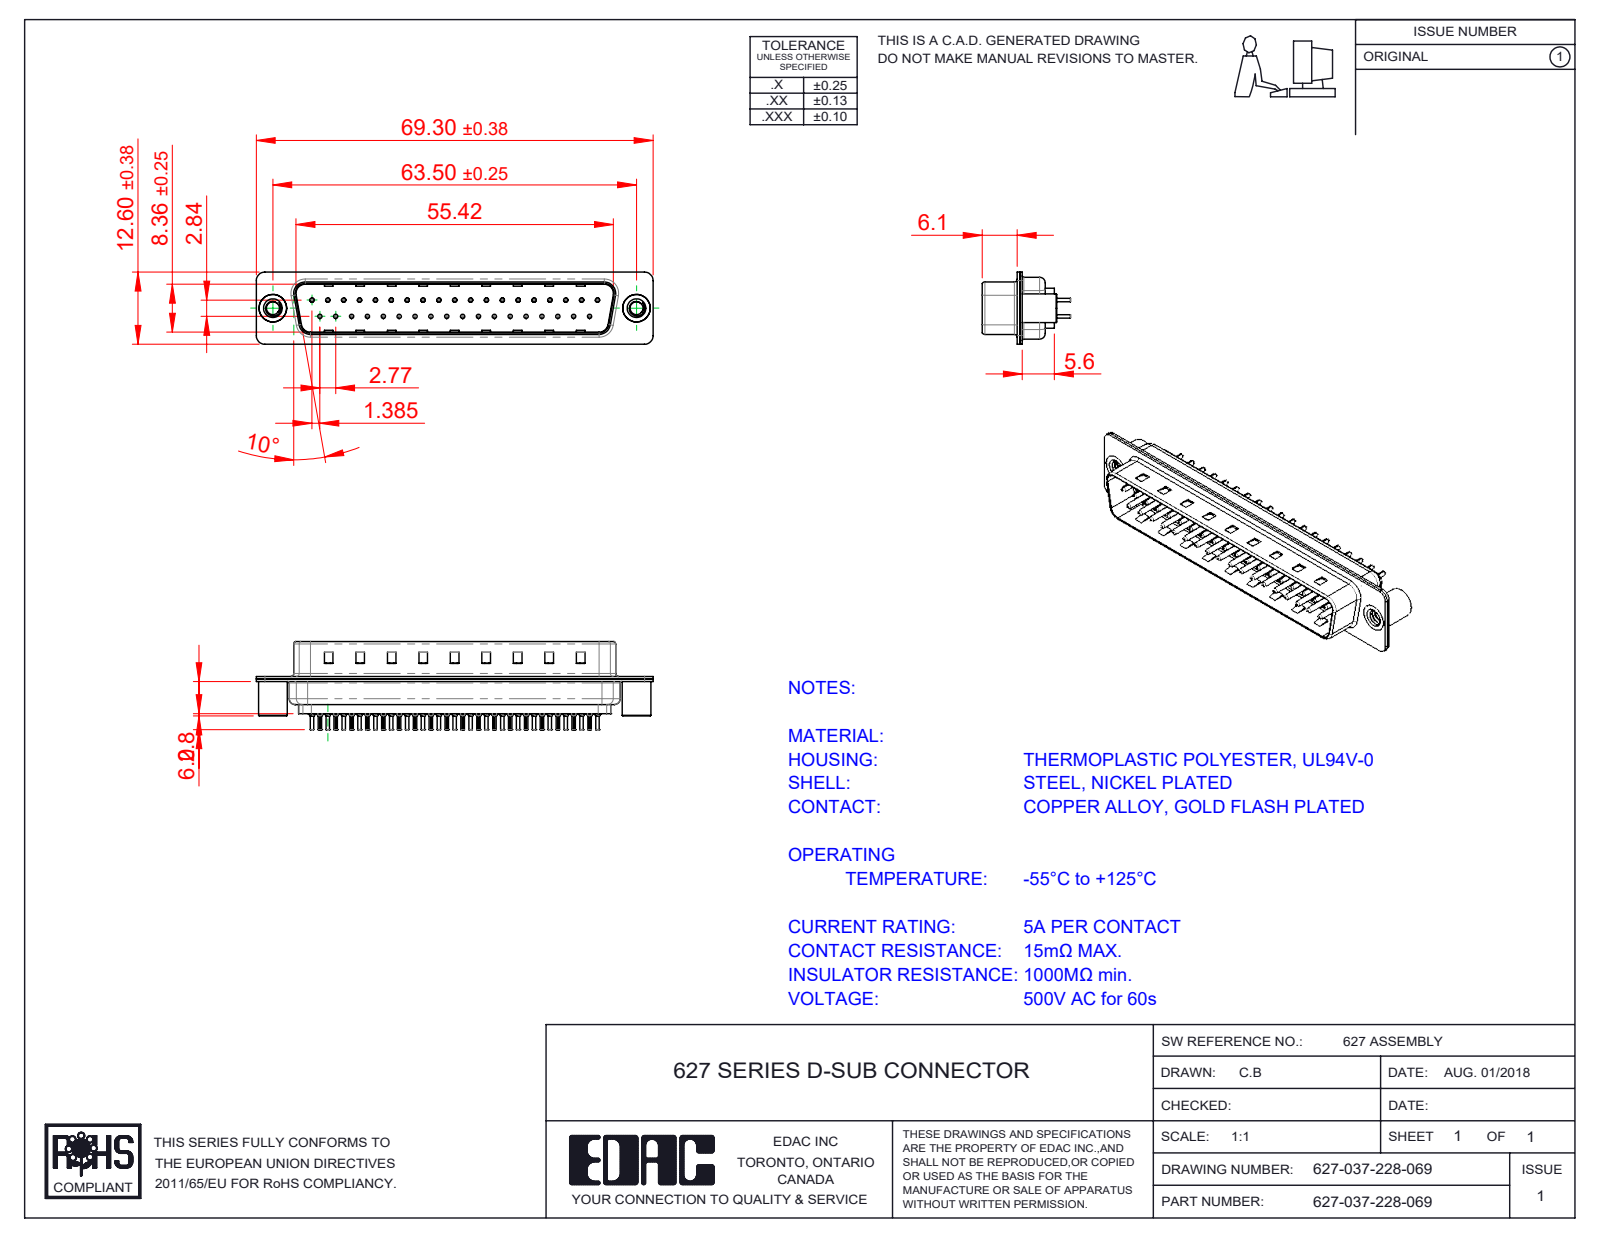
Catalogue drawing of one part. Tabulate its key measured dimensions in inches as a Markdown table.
| quantity | value |
| --- | --- |
| part name | 627-037-228-069; 627 Shell Rear_37 Contacts; 627 Housing_37 FF; 627 4-40 Threaded Standoff BS (+3 more) |
| STEP written by | SolidWorks 2020 (CONFIG_CONTROL_DESIGN) |
| units | inches |
| bodies | 43 solids, 4145 faces (1097 planar, 1609 cylindrical, 1439 other) |
| overall size | 2.728 × 0.74 × 0.496 |
| volume | 0.284 in³ |
| surface area | 19.35 in² |
| round holes (diameter × count) | 0.008 × 37, 0.014 × 37, 0.043 × 37, 0.063 × 37, 0.089 × 2, 0.157 × 2, 0.189 × 2 |
| round bosses / shafts (diameter × count) | 0.079 × 37, 0.059 × 37, 0.03 × 37, 0.024 × 37, 0.197 × 2, 0.193 × 2 |
| partial cylindrical surfaces (radius × count) | 0.004 × 74, 0.059 × 16, 0.079 × 12, 0.02 × 8, 0.063 × 8, 0.01 × 4, 0.024 × 4, 0.026 × 4 |
| main face-to-face distances | 0.016, 0.238, 0.032, 0.377, 0.018, 0.331, 0.027, 0.302, 0.059, 0.043 |
| hole center spacings | 0.124, 0.109, 0.218, 0.327, 0.198, 0.398, 0.436, 0.503 |
